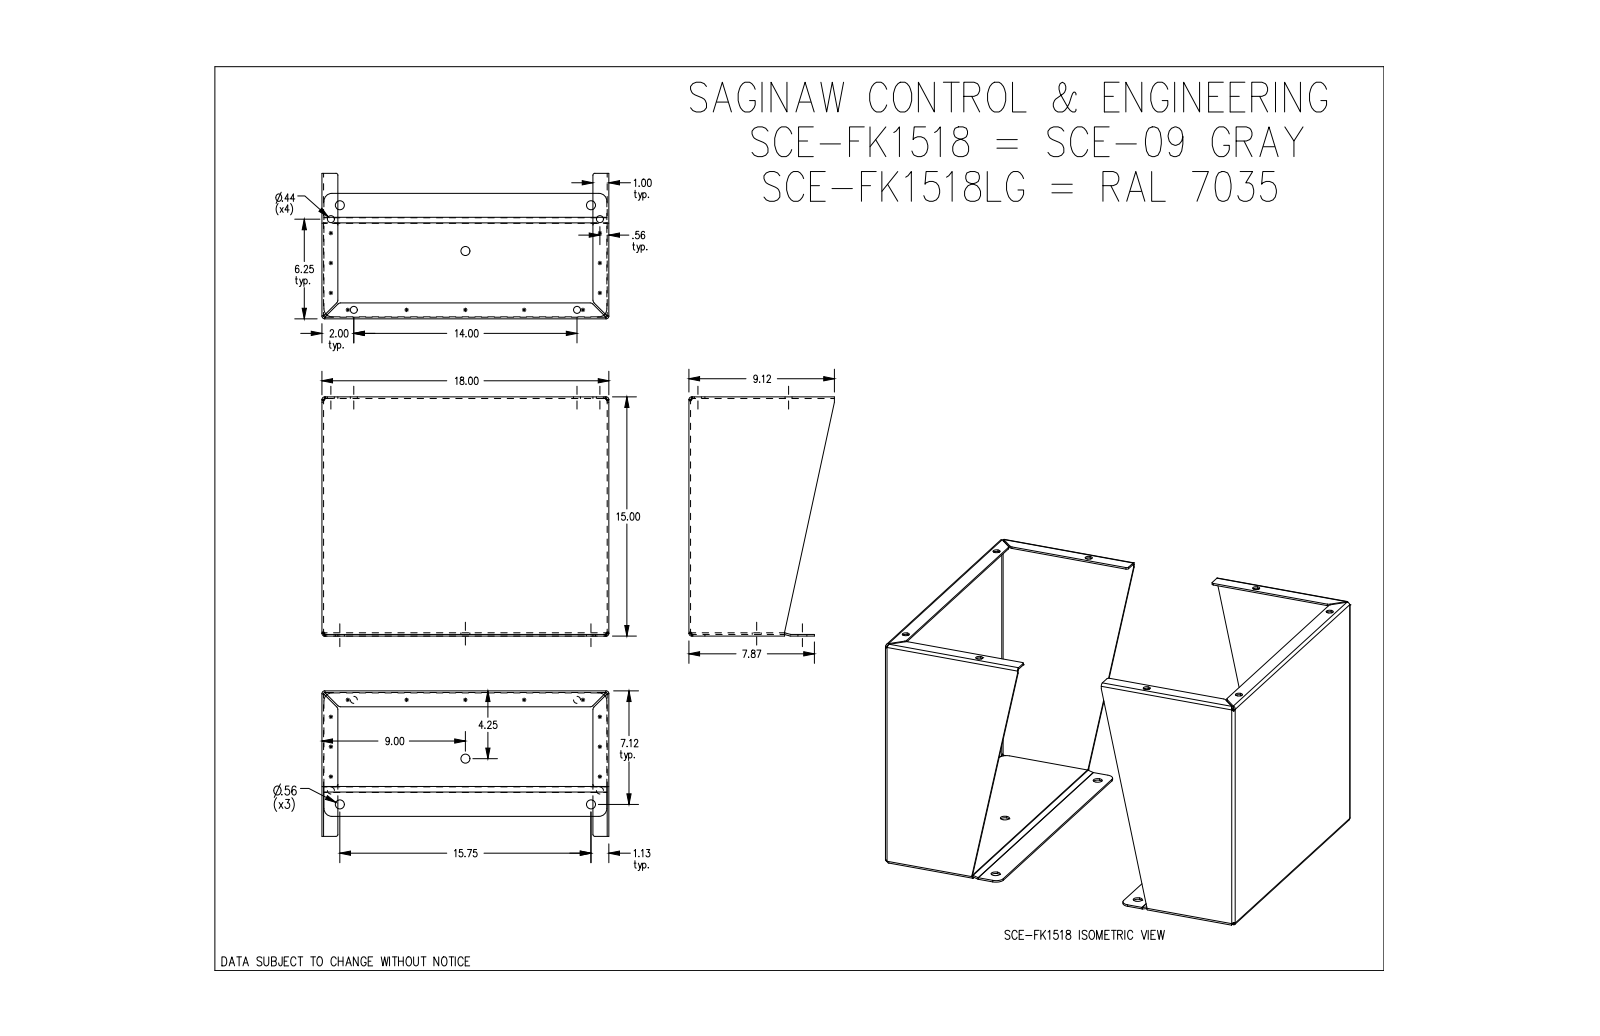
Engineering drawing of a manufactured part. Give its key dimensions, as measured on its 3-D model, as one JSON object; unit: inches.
{"part_name": "SCE-FK1518", "step_written_by": "SolidWorks 2019 (CONFIG_CONTROL_DESIGN)", "units": "inches", "bodies": {"solids": 4, "faces": 214, "planar": 96, "cylindrical": 86, "other": 32}, "overall_size": [24, 18, 15], "volume_in3": 141.5, "surface_area_in2": 2755, "round_holes": [[0.437, 8], [0.563, 6]], "partial_cylinders_radius": [[0.166, 16], [0.062, 12], [0.125, 8], [0.22, 8], [0.5, 8], [0.063, 6]], "face_to_face_distances": [0.104, 23.896, 17.896, 24, 23.792, 18, 17.792, 14.792, 0.101, 14.893], "hole_center_spacings": [1.035, 5.866, 6.614, 7.913, 8.671, 10.646, 14.884, 15.919]}
